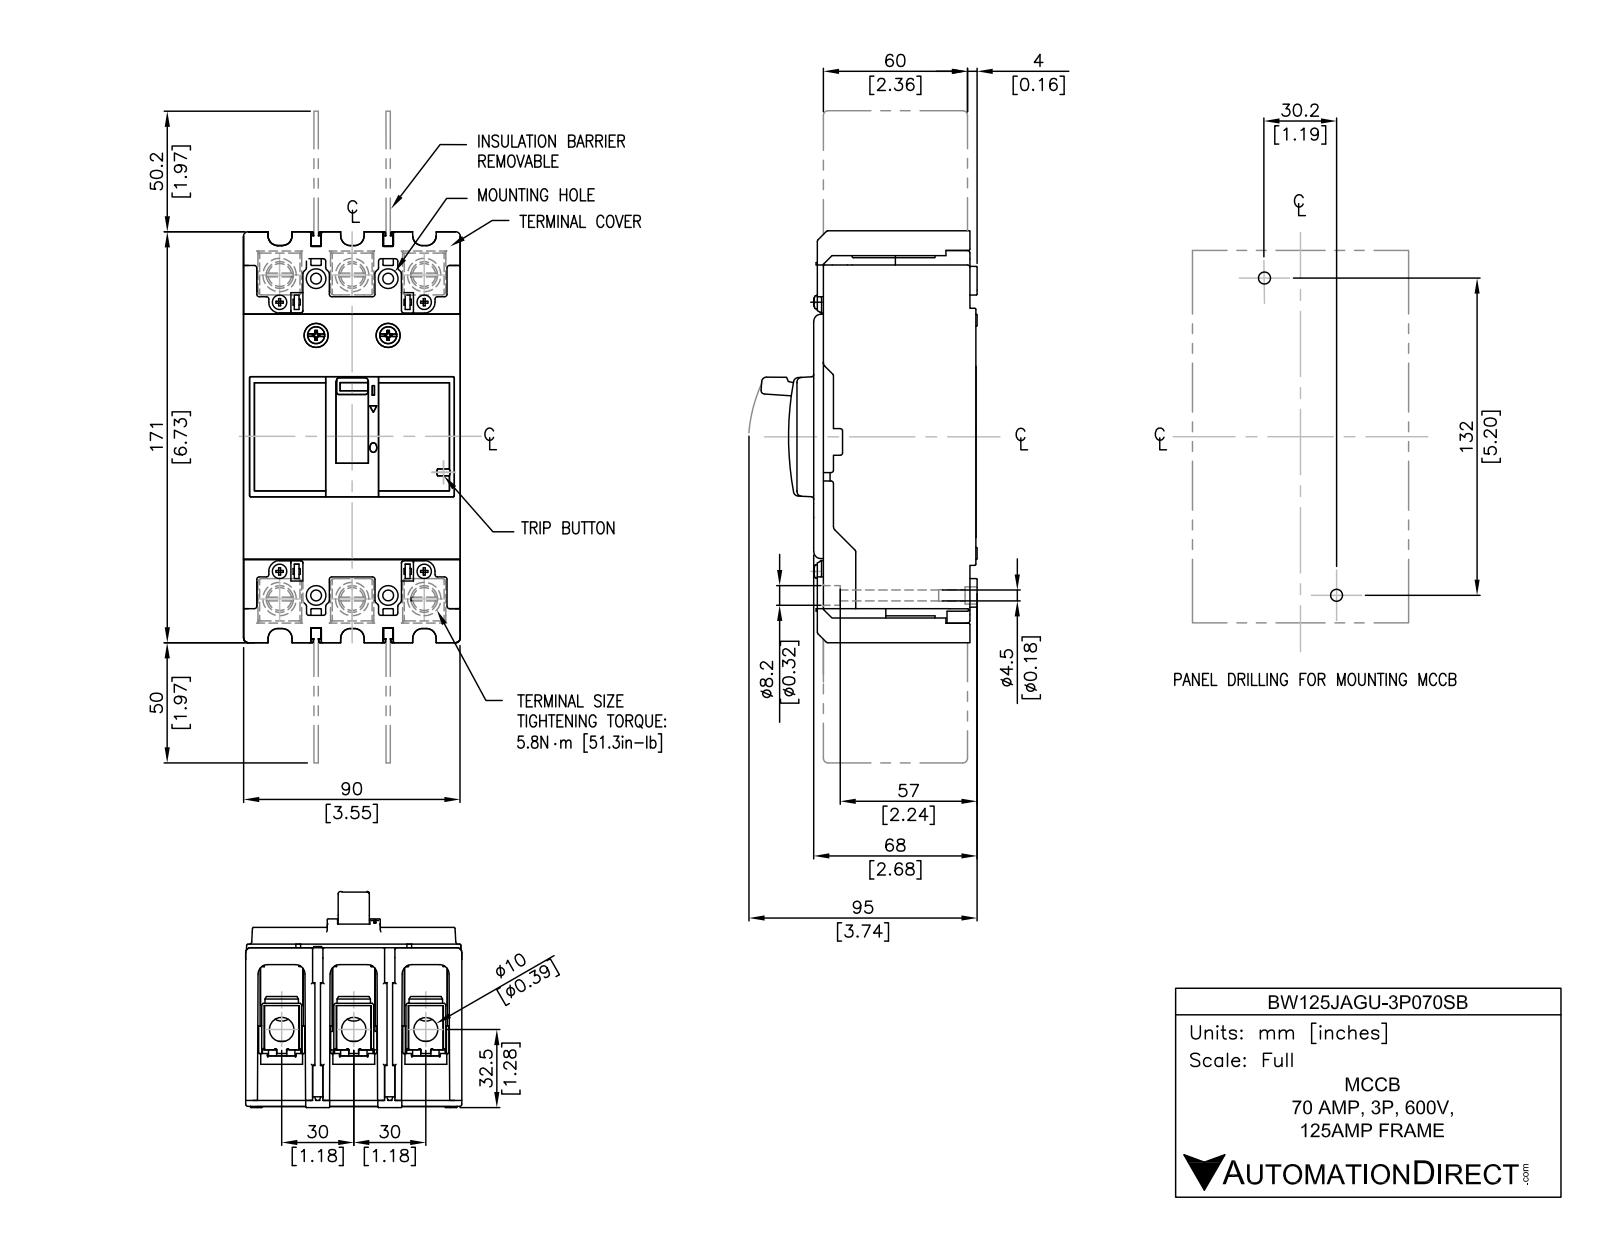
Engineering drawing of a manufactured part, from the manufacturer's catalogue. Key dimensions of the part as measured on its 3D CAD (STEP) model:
Part name (STEP PRODUCT): BW125JAGU-3P070SB
STEP written by: SolidWorks 2018 (AUTOMOTIVE_DESIGN)
Units: inches
Bodies: 14 solids, 452 faces (340 planar, 88 cylindrical, 24 other)
Overall size (bounding box): 10.197 × 3.602 × 3.543
Volume: 57.4 in³ · Surface area: 230.3 in²
Round holes (diameter × count): ⌀0.315 ×6, ⌀0.177 ×4, ⌀0.323 ×4
Round bosses / shafts (diameter × count): ⌀0.472 ×6
Partial cylindrical surfaces — rounded edges, fillets, slot ends (radius × count): R0.157 ×12, R0.079 ×6, R0.118 ×6
Main face-to-face distances: 1.181, 1.11, 1.252, 2.291, 2.433, 0.142, 3.543, 0.236, 2.402, 1.039
Hole centre spacings: 0.593, 5.289, 1.181, 1.772, 5.444, 5.546, 5.315, 2.362
